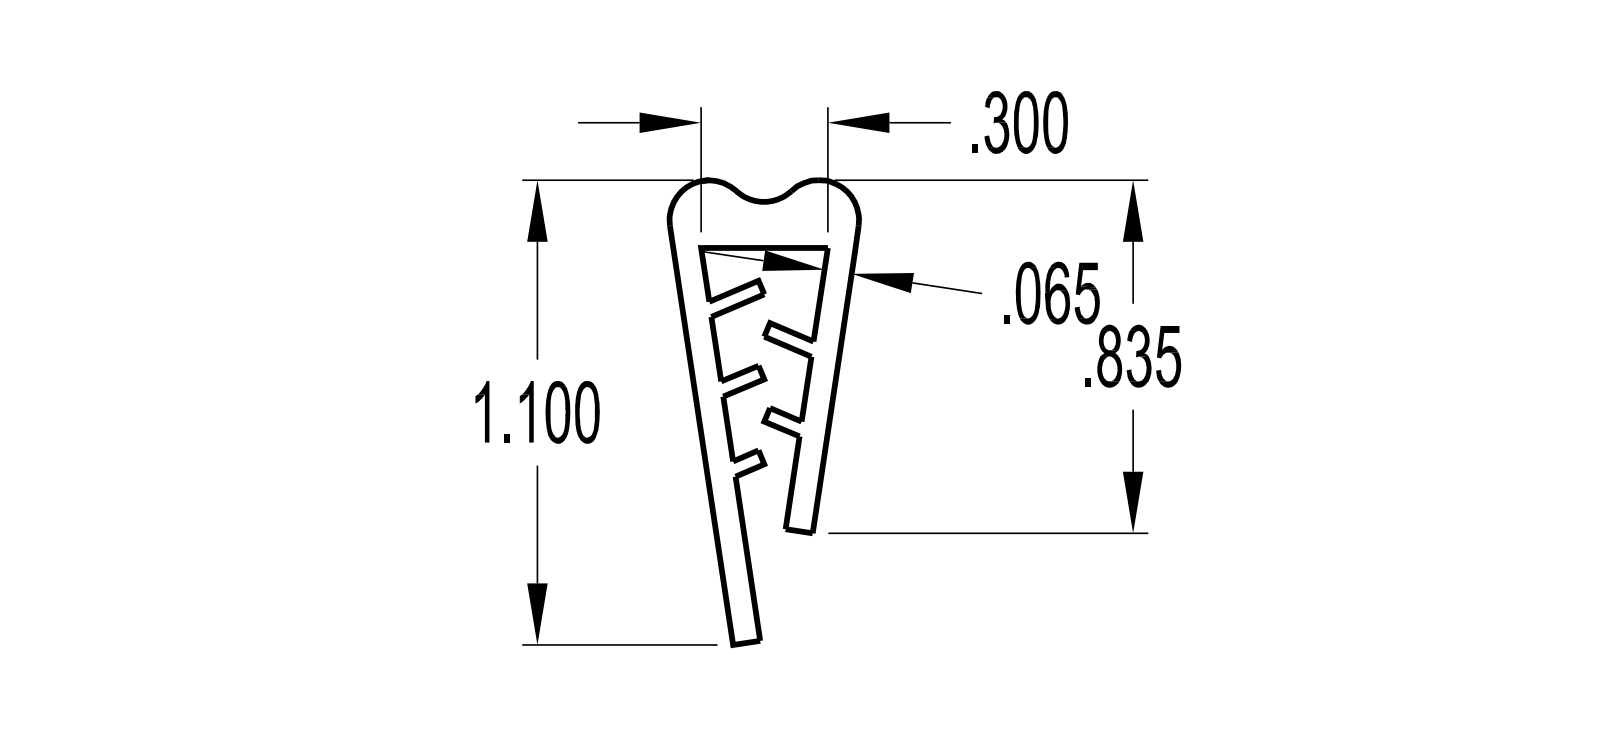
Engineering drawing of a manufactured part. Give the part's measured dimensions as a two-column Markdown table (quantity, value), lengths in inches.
| quantity | value |
| --- | --- |
| STEP written by | KeyCreator Pro (AUTOMOTIVE_DESIGN) |
| units | inches |
| bodies | 1 solid, 32 faces (29 planar, 3 cylindrical, 0 other) |
| overall size | 6 × 1.1 × 0.449 |
| volume | 1.104 in³ |
| surface area | 32.75 in² |
| partial cylindrical surfaces (radius × count) | 0.094 × 2, 0.095 × 1 |
| main face-to-face distances | 0.065, 0.185, 0.035, 0.22, 0.15, 0.37, 0.065, 0.078, 0.405, 0.335 |
